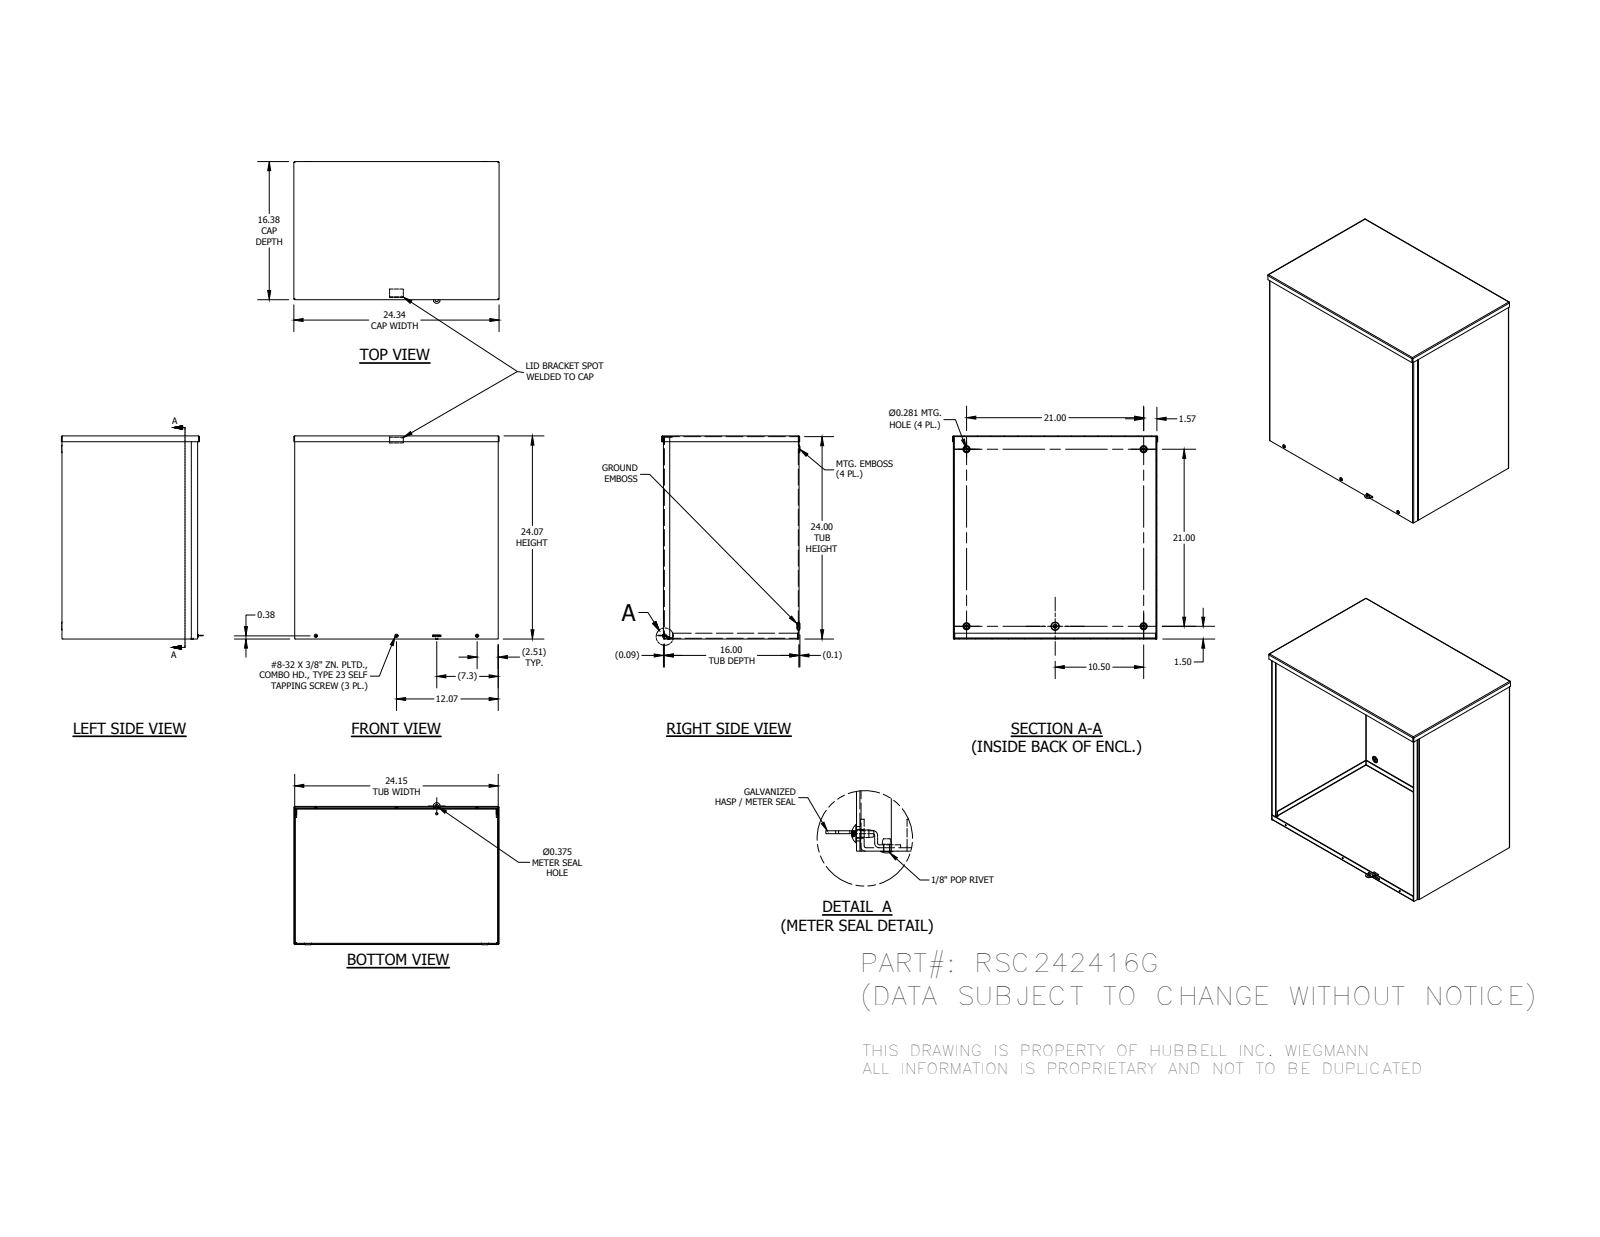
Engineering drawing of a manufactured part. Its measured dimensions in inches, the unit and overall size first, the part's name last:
Units: inches
Overall size (bounding box): 24.335 × 24.114 × 16.85
Round holes (diameter × count): ⌀0.313 ×6, ⌀0.281 ×4, ⌀0.147 ×3, ⌀0.125 ×1, ⌀0.136 ×1, ⌀0.171 ×1, ⌀0.375 ×1
Round bosses / shafts (diameter × count): ⌀0.384 ×3, ⌀0.164 ×3, ⌀0.262 ×1, ⌀0.233 ×1, ⌀0.125 ×1
Partial cylindrical surfaces — rounded edges, fillets, slot ends (radius × count): R0.031 ×19, R0.105 ×17, R0.093 ×2, R0.4 ×1
Main face-to-face distances: 0.074, 24, 16.016, 24.074, 16.09, 15.942, 23.926, 24.148, 0.155, 23.919
Hole centre spacings: 9.563, 10.56, 20.094, 21, 25.14, 23.25, 1.464, 1.465
Volume: 209.6 in³ · Surface area: 5 699 in²
Bodies: 10 solids, 350 faces (193 planar, 66 cylindrical, 91 other)
Part name (STEP PRODUCT): RSC242416GBKPA; RSC2416GEWPA; RSC2424GLFA; RSC2416GCPA (+5 more)
STEP written by: Autodesk Inventor 2014 (AUTOMOTIVE_DESIGN)
